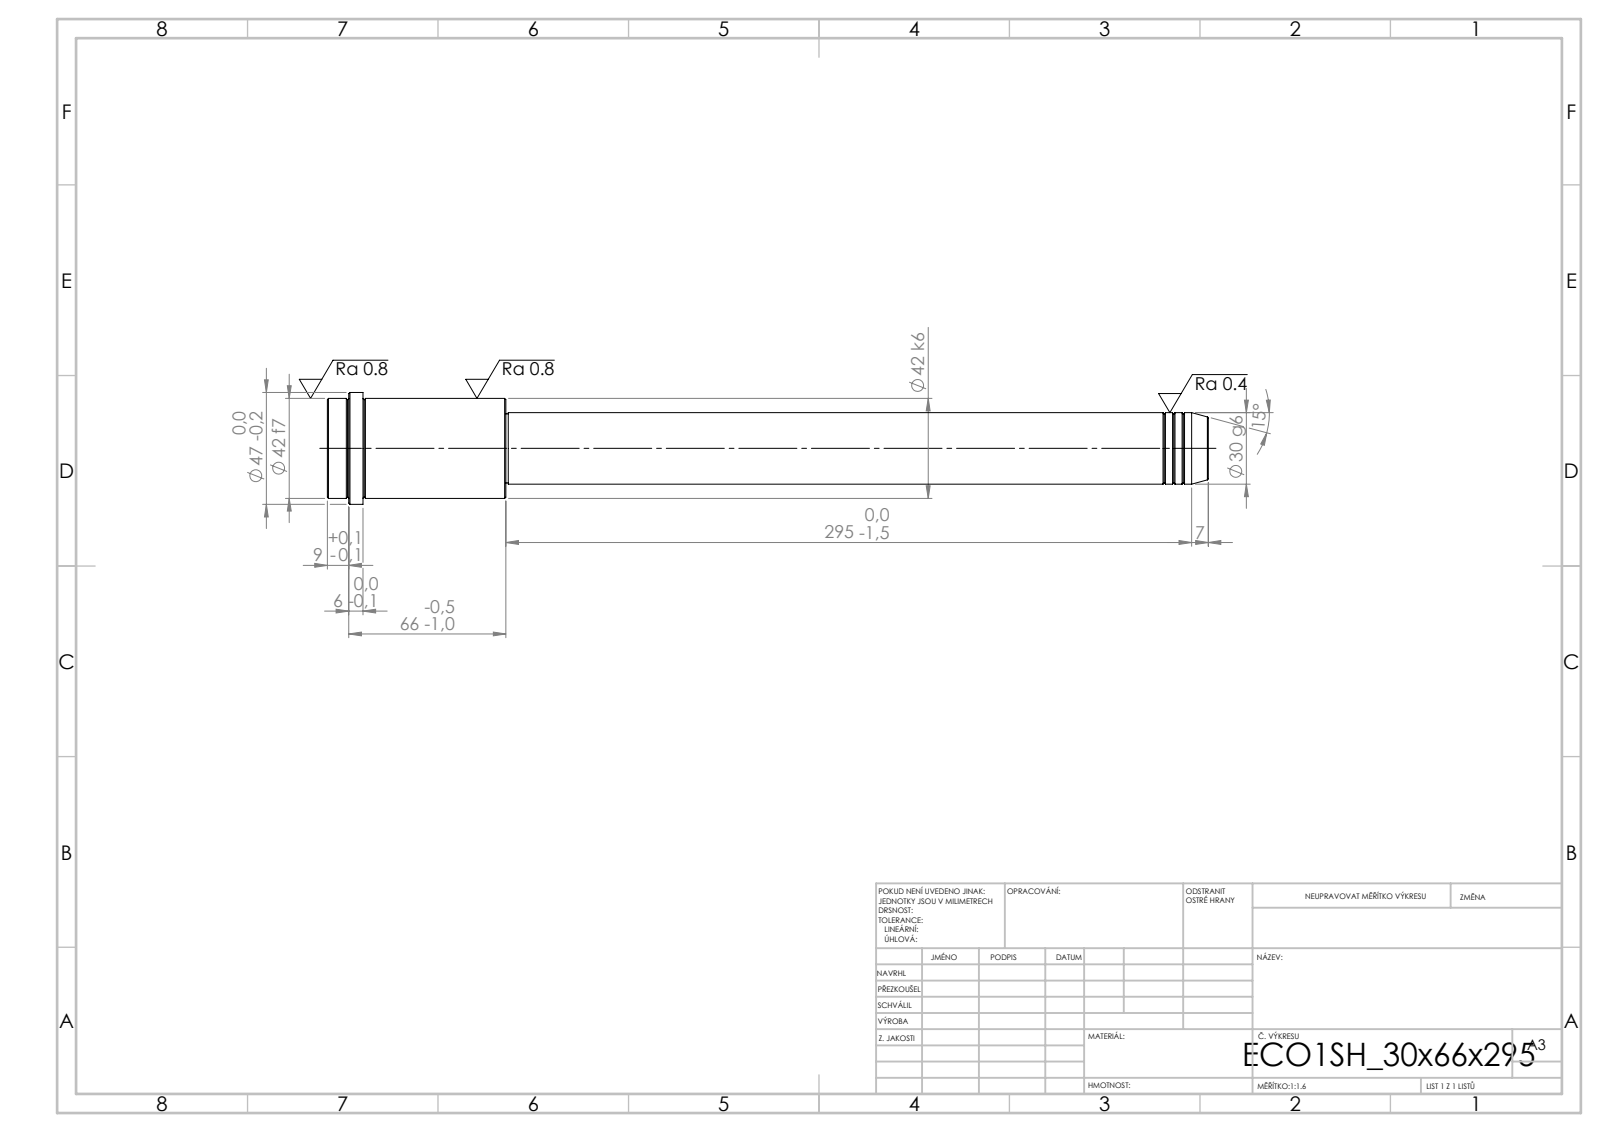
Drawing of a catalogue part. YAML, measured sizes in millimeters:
step_written_by: "SolidWorks 2019 (CONFIG_CONTROL_DESIGN)"
units: millimeters
bodies: {solids: 1, faces: 52, planar: 6, cylindrical: 16, other: 30}
overall_size: [370, 47, 47]
volume: 313624
surface_area: 41333
round_bosses_or_shafts:
  - {diameter: 47, count: 1}
  - {diameter: 42, count: 1}
  - {diameter: 30, count: 1}
  - {diameter: 29, count: 1}
face_to_face_distances: [75, 295, 370, 355, 60, 15, 361, 66, 6, 9]
